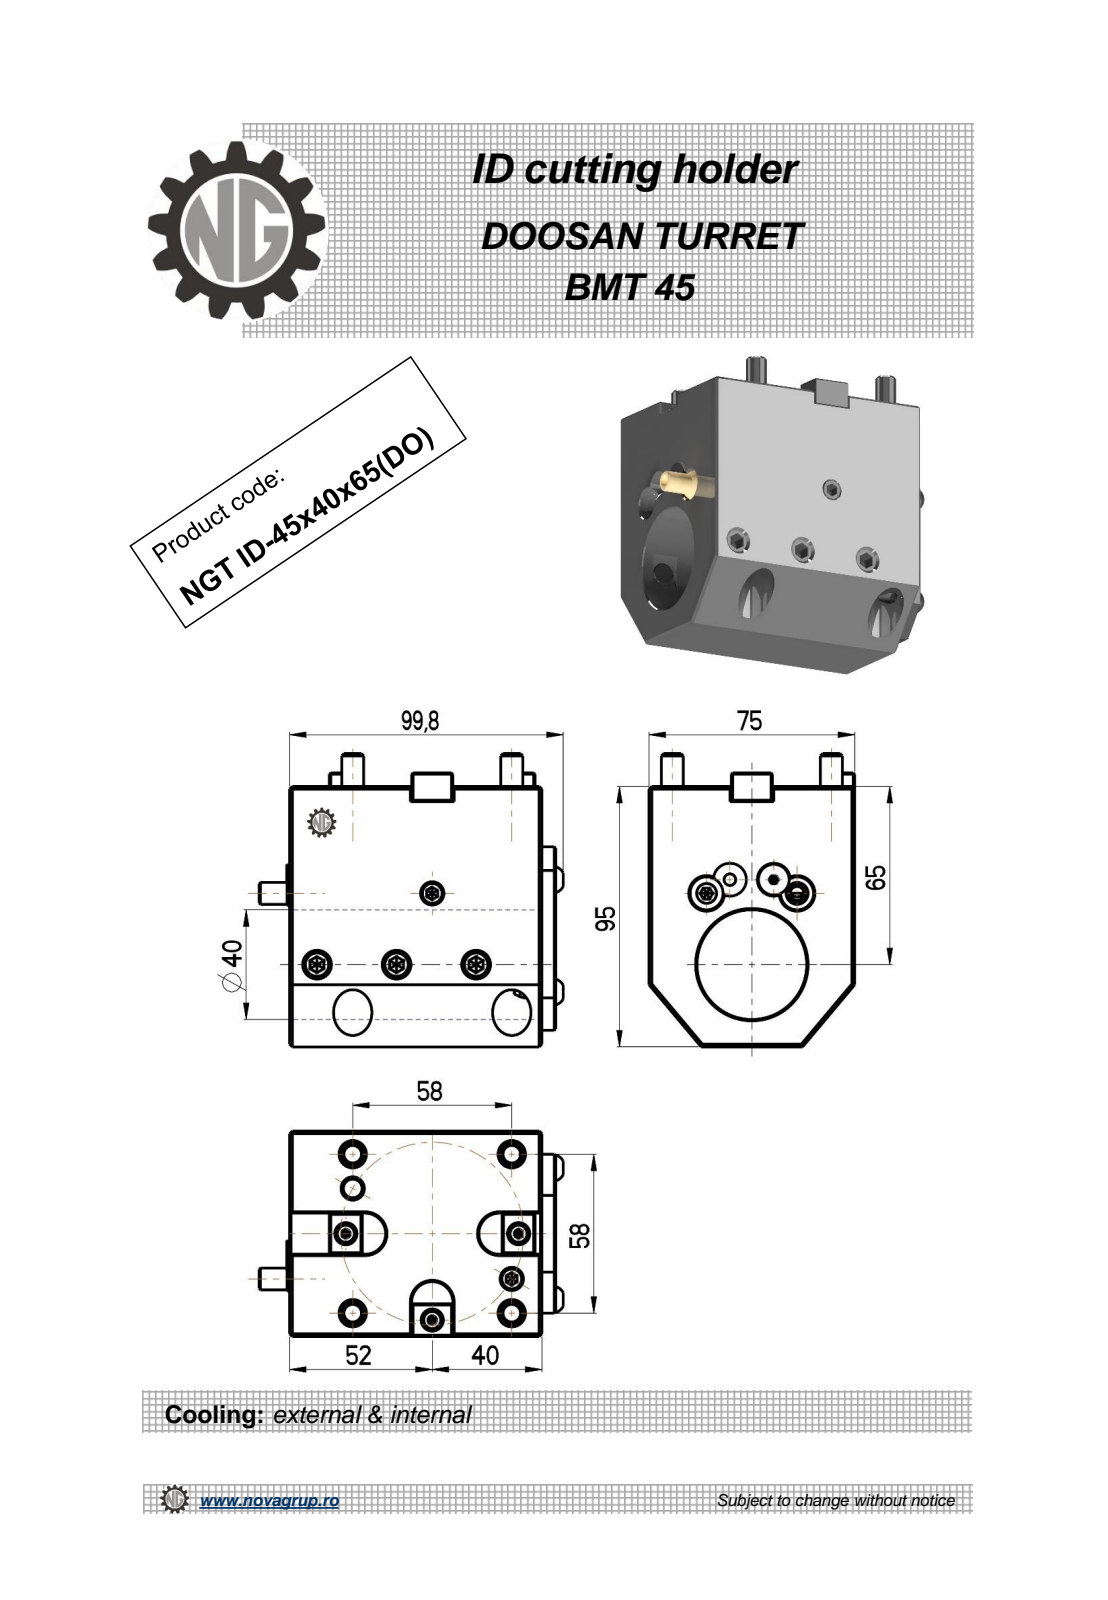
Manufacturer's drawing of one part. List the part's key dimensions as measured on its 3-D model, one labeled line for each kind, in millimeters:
Part name (STEP PRODUCT): NGT_ID_45_40_65_DO
STEP written by: PRO/ENGINEER BY PARAMETRIC TECHNOLOGY CORPORATION, 2010280 (CONFIG_CONTROL_DESIGN)
Units: millimetres
Bodies: 1 solid, 386 faces (194 planar, 93 cylindrical, 99 other)
Overall size (bounding box): 110.88 × 107 × 75
Volume: 518 413 mm³ · Surface area: 59 913 mm²
Round holes (diameter × count): ⌀8.5 ×3, ⌀5 ×1, ⌀6.8 ×1, ⌀40 ×1
Round bosses / shafts (diameter × count): ⌀8 ×5, ⌀11.2 ×1
Partial cylindrical surfaces — rounded edges, fillets, slot ends (radius × count): R0.51 ×36, R0.22 ×6, R0.41 ×6, R7.5 ×3
Main face-to-face distances: 75, 5, 92, 95, 97, 8.5, 12, 30, 45, 58
Hole centre spacings: 29, 30.79, 58
